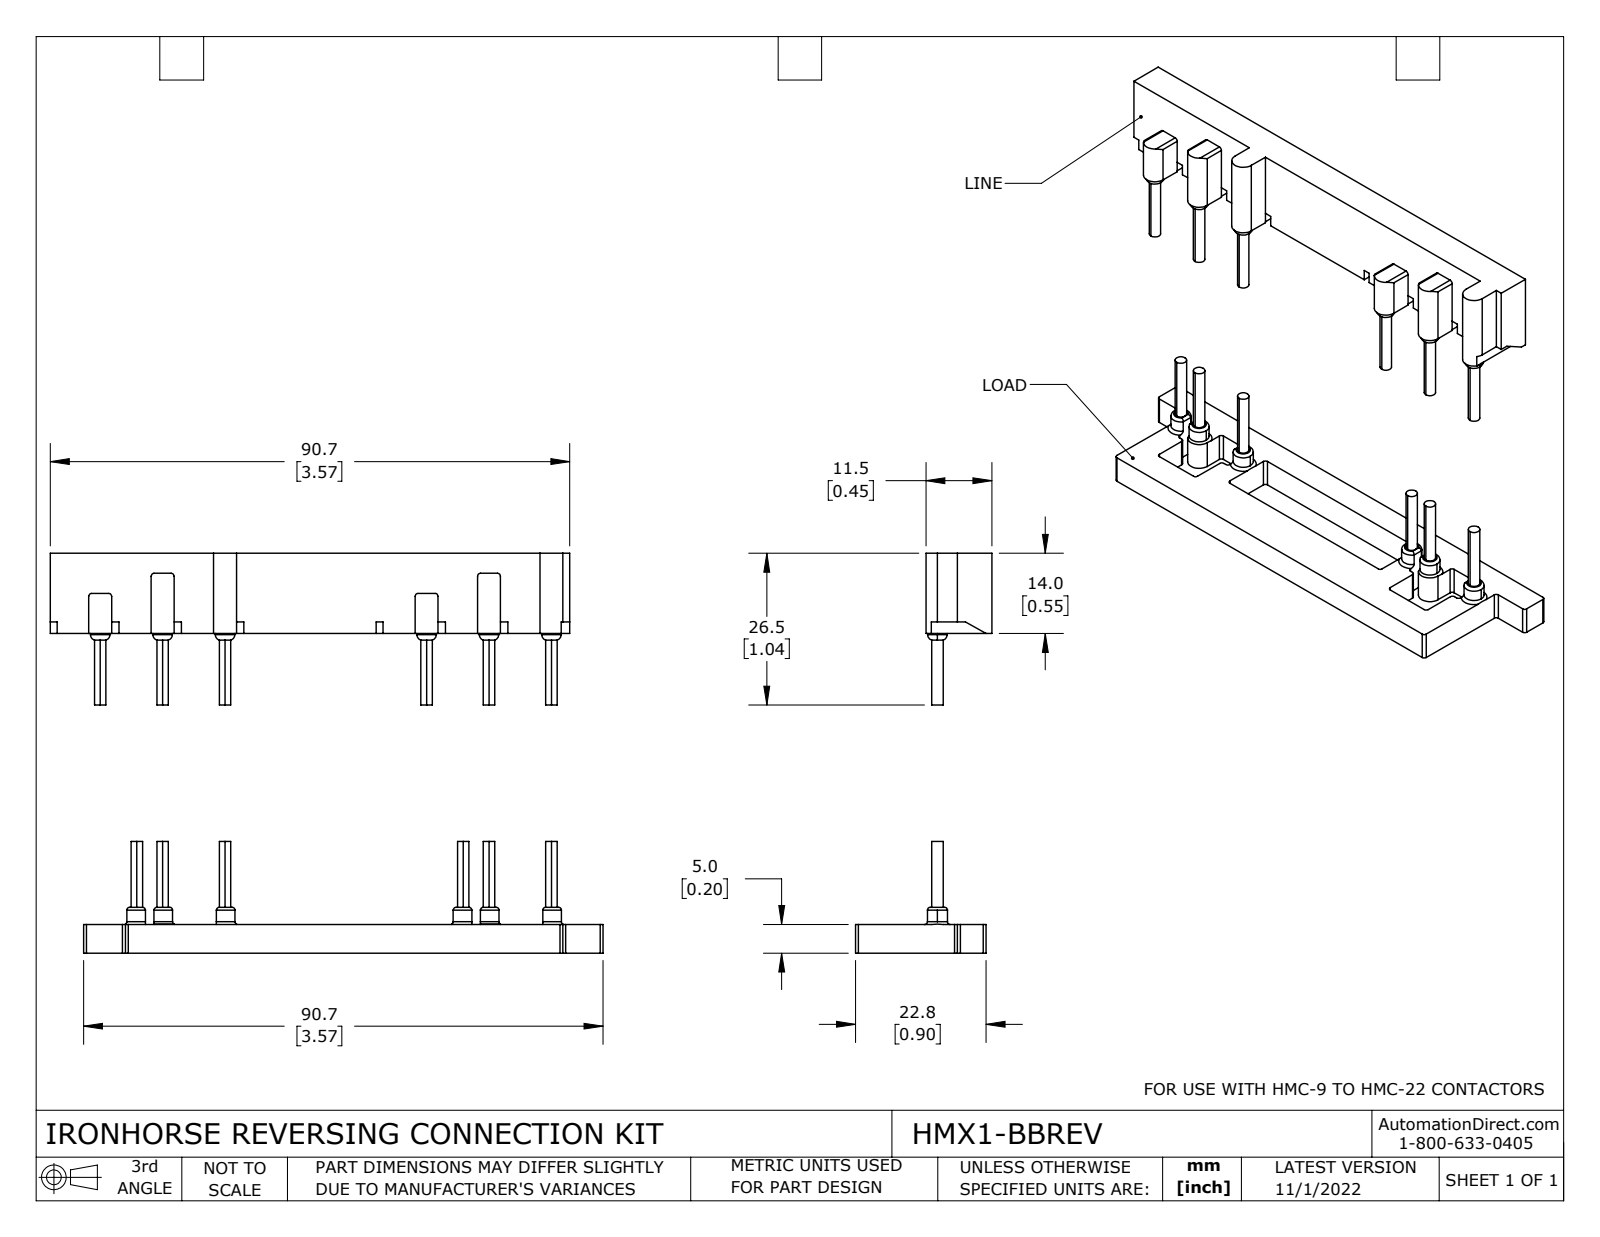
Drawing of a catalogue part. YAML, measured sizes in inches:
part_name: "HMX1-BBREV"
step_written_by: "SolidWorks 2021 (CONFIG_CONTROL_DESIGN)"
units: inches
bodies: {solids: 8, faces: 244, planar: 120, cylindrical: 100, other: 24}
overall_size: [3.799, 2.748, 0.937]
volume: 0.955
surface_area: 16.27
round_bosses_or_shafts:
  - {diameter: 0.079, count: 8}
  - {diameter: 0.138, count: 6}
  - {diameter: 0.134, count: 6}
partial_cylinders:
  - {radius: 0.02, count: 46}
  - {radius: 0.079, count: 6}
face_to_face_distances: [0.197, 0.236, 2, 2.197, 0.551, 2.551, 2.748, 0.039, 2.244, 0.937]
